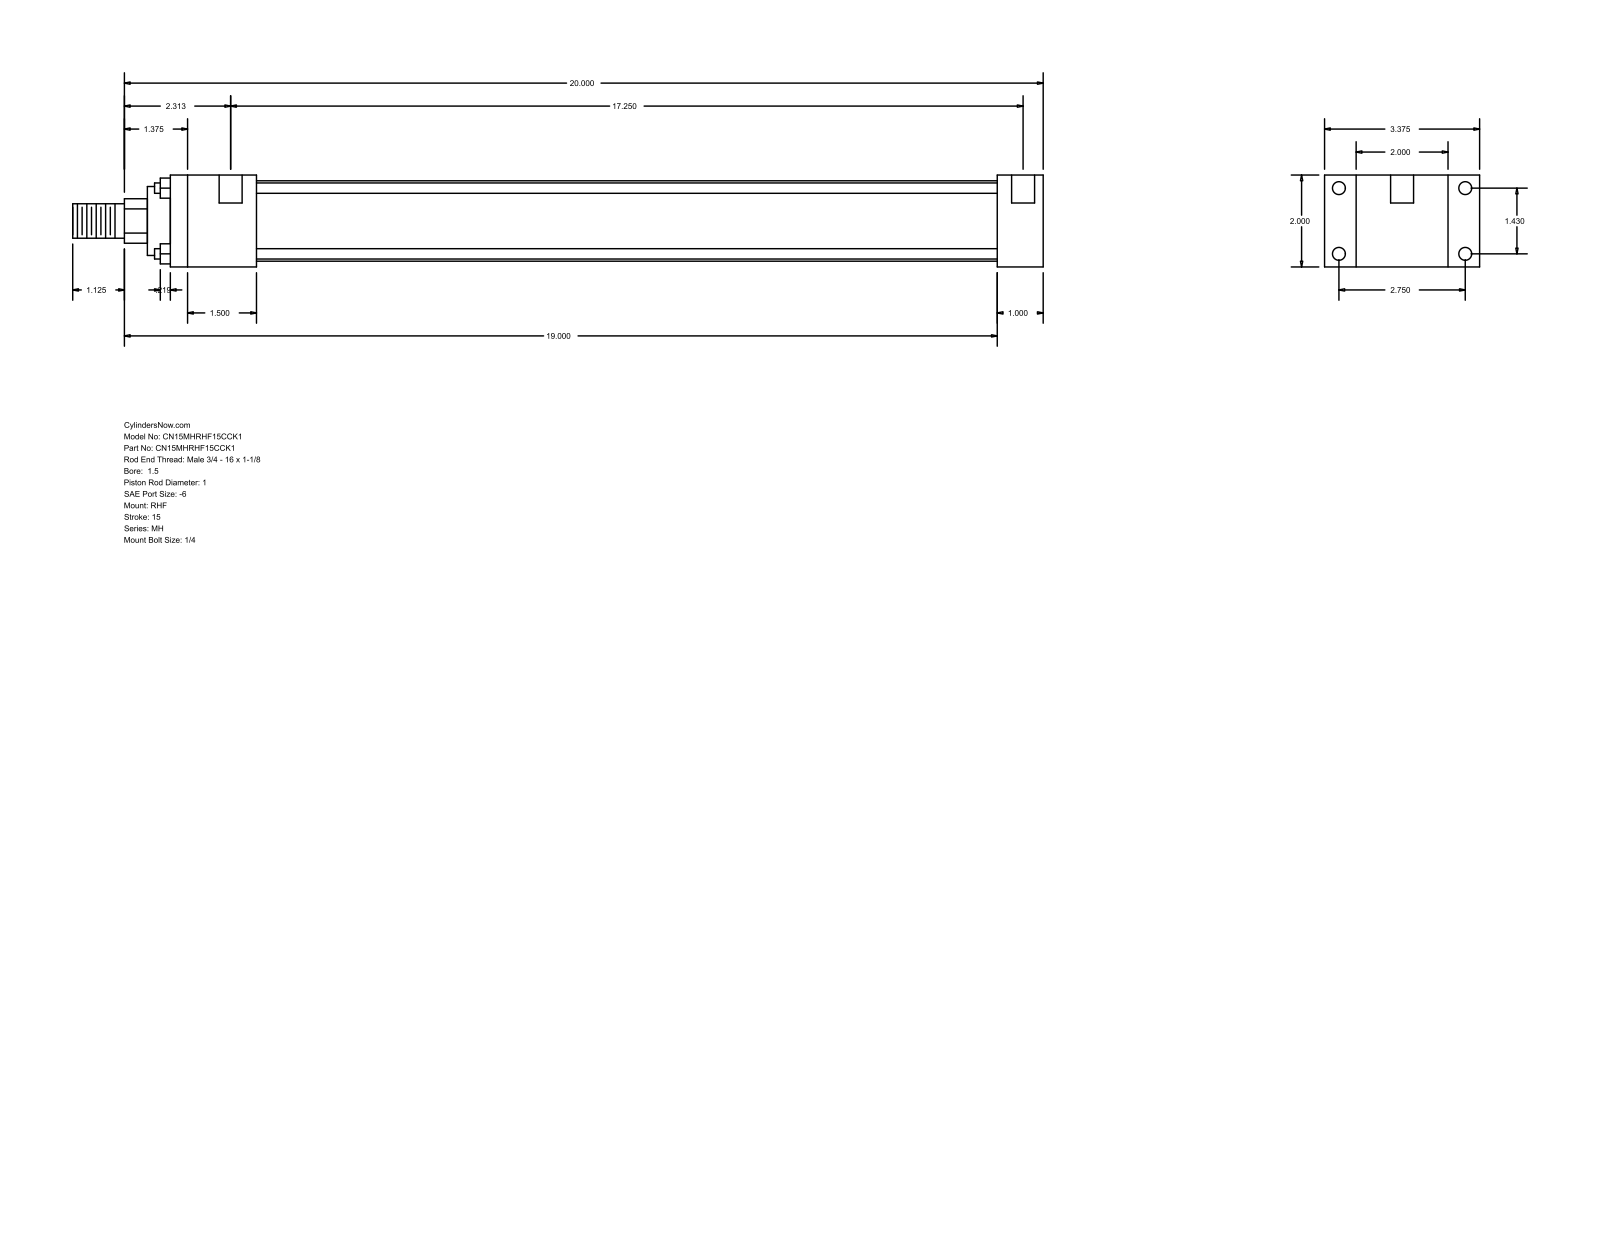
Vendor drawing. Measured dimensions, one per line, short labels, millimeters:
name: MH_RHF__0150_1
written by: GSSL Pune (CONFIG_CONTROL_DESIGN)
unit: mm
bodies: 0 solids, 88 faces (60 planar, 28 cylindrical, 0 other)
size: 536.58 × 85.72 × 50.8
holes: 4× ⌀5.56, 4× ⌀7.14, 2× ⌀12.7
bosses: 4× ⌀5.71, 1× ⌀44.45, 1× ⌀38.1, 1× ⌀25.4, 1× ⌀19.05
rounds: 1× R12.29
face distances: 50.8, 25.4, 17.46, 68.26, 85.72, 482.6, 457.2, 47.63, 409.57, 434.97
hole spacings: 36.32, 69.84, 78.72, 441.33, 3.18, 438.15
